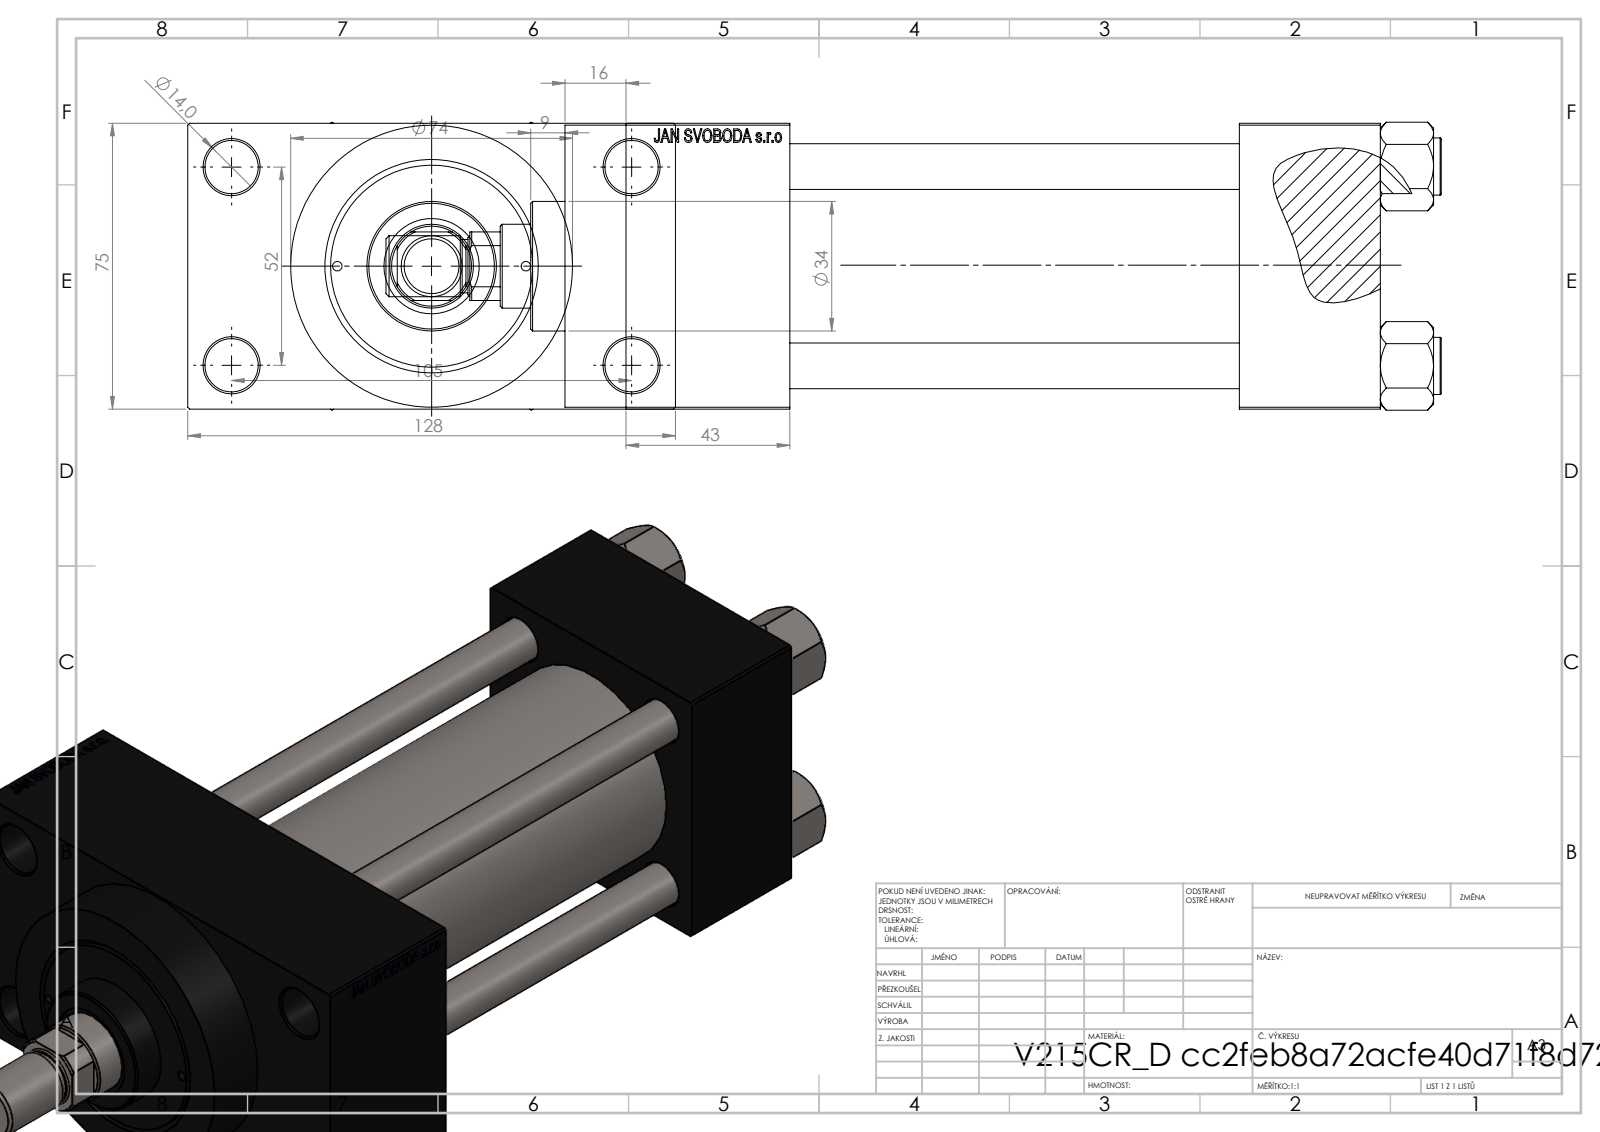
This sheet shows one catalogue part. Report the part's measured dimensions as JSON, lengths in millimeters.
{"part_name": "ROD_END_AH; NUT_M5_D; V215CR_VCP_D; V215CR_D_TYCINKA (+2 more)", "step_written_by": "SolidWorks 2019 (CONFIG_CONTROL_DESIGN)", "units": "millimeters", "bodies": {"solids": 12, "faces": 1125, "planar": 503, "cylindrical": 96, "other": 526}, "overall_size": [277, 128, 75.54], "volume_mm3": 881510, "surface_area_mm2": 201338, "round_holes": [[12, 4], [14, 4], [2.5, 2], [7, 2], [20.96, 2], [30, 2], [10.5, 1], [22, 1], [25, 1], [41, 1], [50, 1], [53, 1]], "round_bosses_or_shafts": [[15, 4], [74, 1], [56, 1], [34, 1], [16, 1], [14, 1]], "partial_cylinders_radius": [[10.5, 1]], "face_to_face_distances": [75, 118, 37, 155, 26.5, 198, 161, 43, 101.5, 16], "hole_center_spacings": [26.19, 26.35, 36.98, 38.03, 52.3, 57.22, 58.43, 58.59]}
